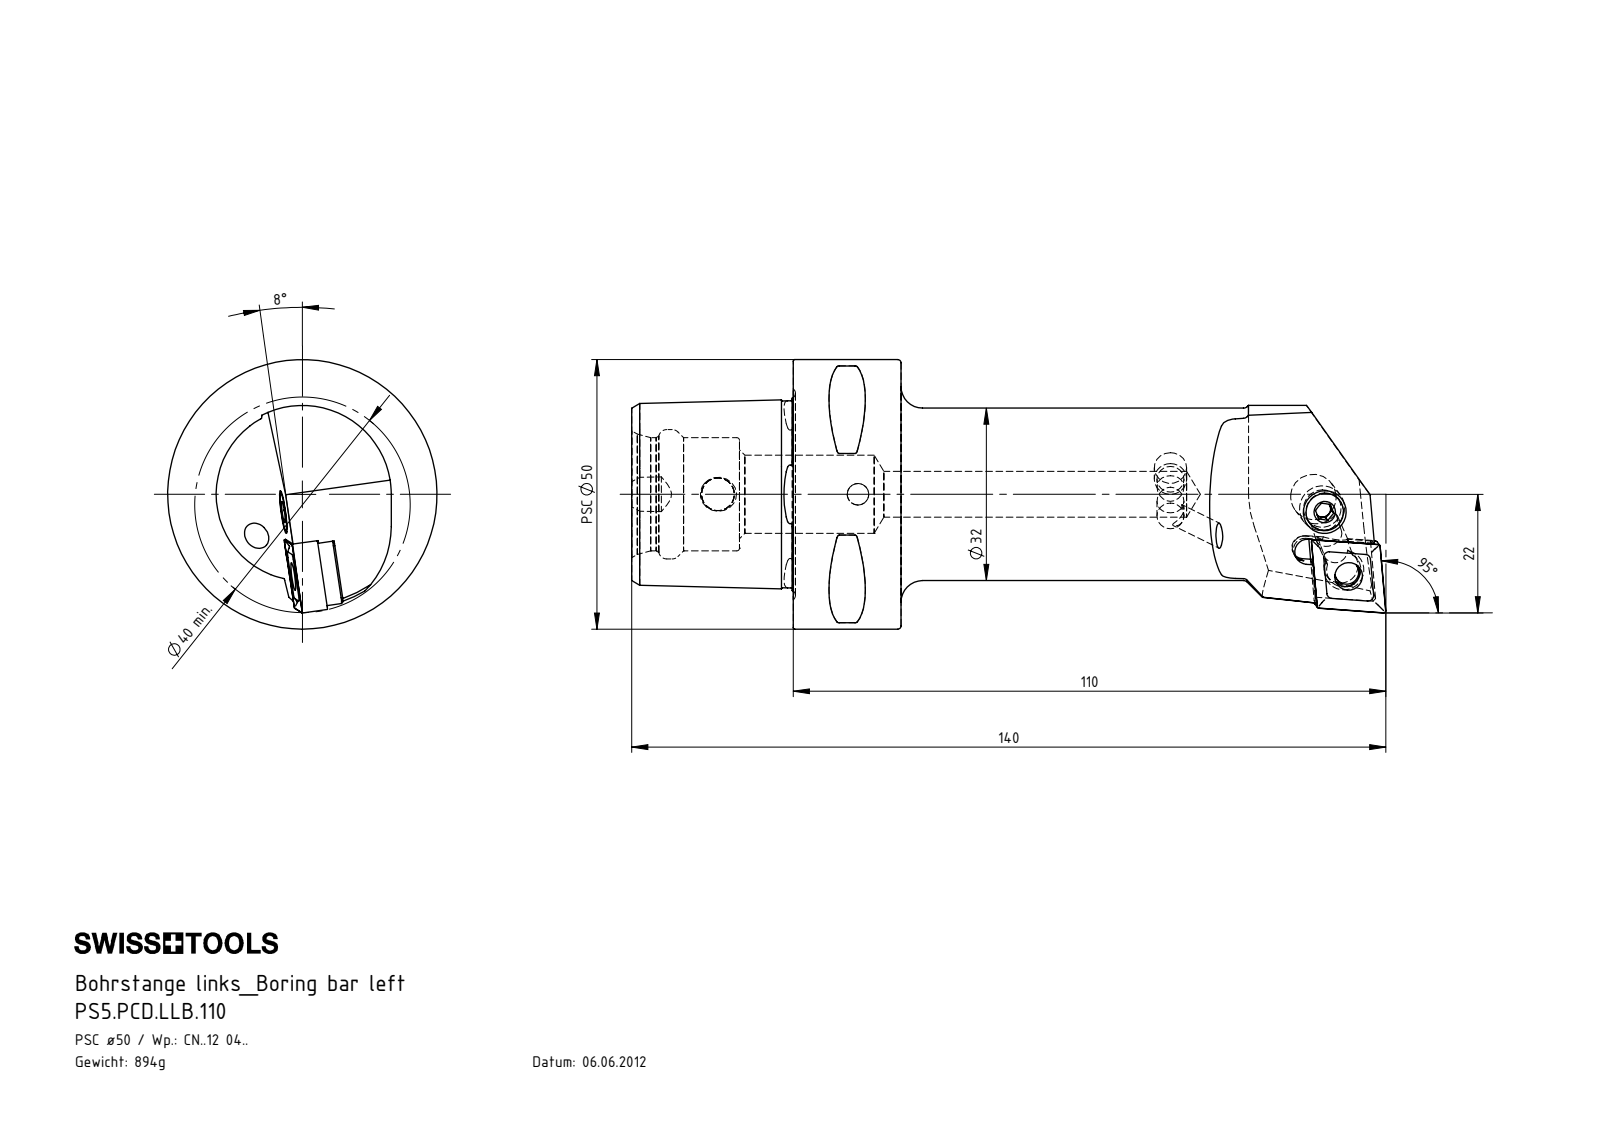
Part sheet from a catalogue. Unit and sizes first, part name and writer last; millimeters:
Units: millimetres
Overall size (bounding box): 140 × 50 × 50
Round holes (diameter × count): ⌀4 ×1, ⌀4.2 ×1, ⌀5 ×1, ⌀5.16 ×1, ⌀6.1 ×1, ⌀6.4 ×1, ⌀7 ×1, ⌀8.4 ×1, ⌀8.5 ×1, ⌀14.5 ×1, ⌀21 ×1, ⌀24 ×1
Round bosses / shafts (diameter × count): ⌀50 ×1, ⌀32 ×1, ⌀8 ×1, ⌀7.9 ×1, ⌀6.4 ×1, ⌀6 ×1, ⌀4.5 ×1, ⌀3.55 ×1
Partial cylindrical surfaces — rounded edges, fillets, slot ends (radius × count): R0.5 ×8, R0.4 ×4, R1 ×4, R2.5 ×2, R2.1 ×1, R2.2 ×1, R2.35 ×1, R2.8 ×1
Main face-to-face distances: 20, 30, 50, 4.49, 19.18, 3.18, 7.67, 44.4, 10, 0.5
Hole centre spacings: 12.8, 12.86, 26
Volume: 113 093 mm³ · Surface area: 26 186 mm²
Bodies: 9 solids, 362 faces (96 planar, 92 cylindrical, 174 other)
Part name (STEP PRODUCT): KVT_MB_600_060; WCD-ER2.101.003_A; PS5-PCD.LLB.110; WCD-ER1.101.000 (+4 more)
STEP written by: SolidWorks 2012 (CONFIG_CONTROL_DESIGN)
